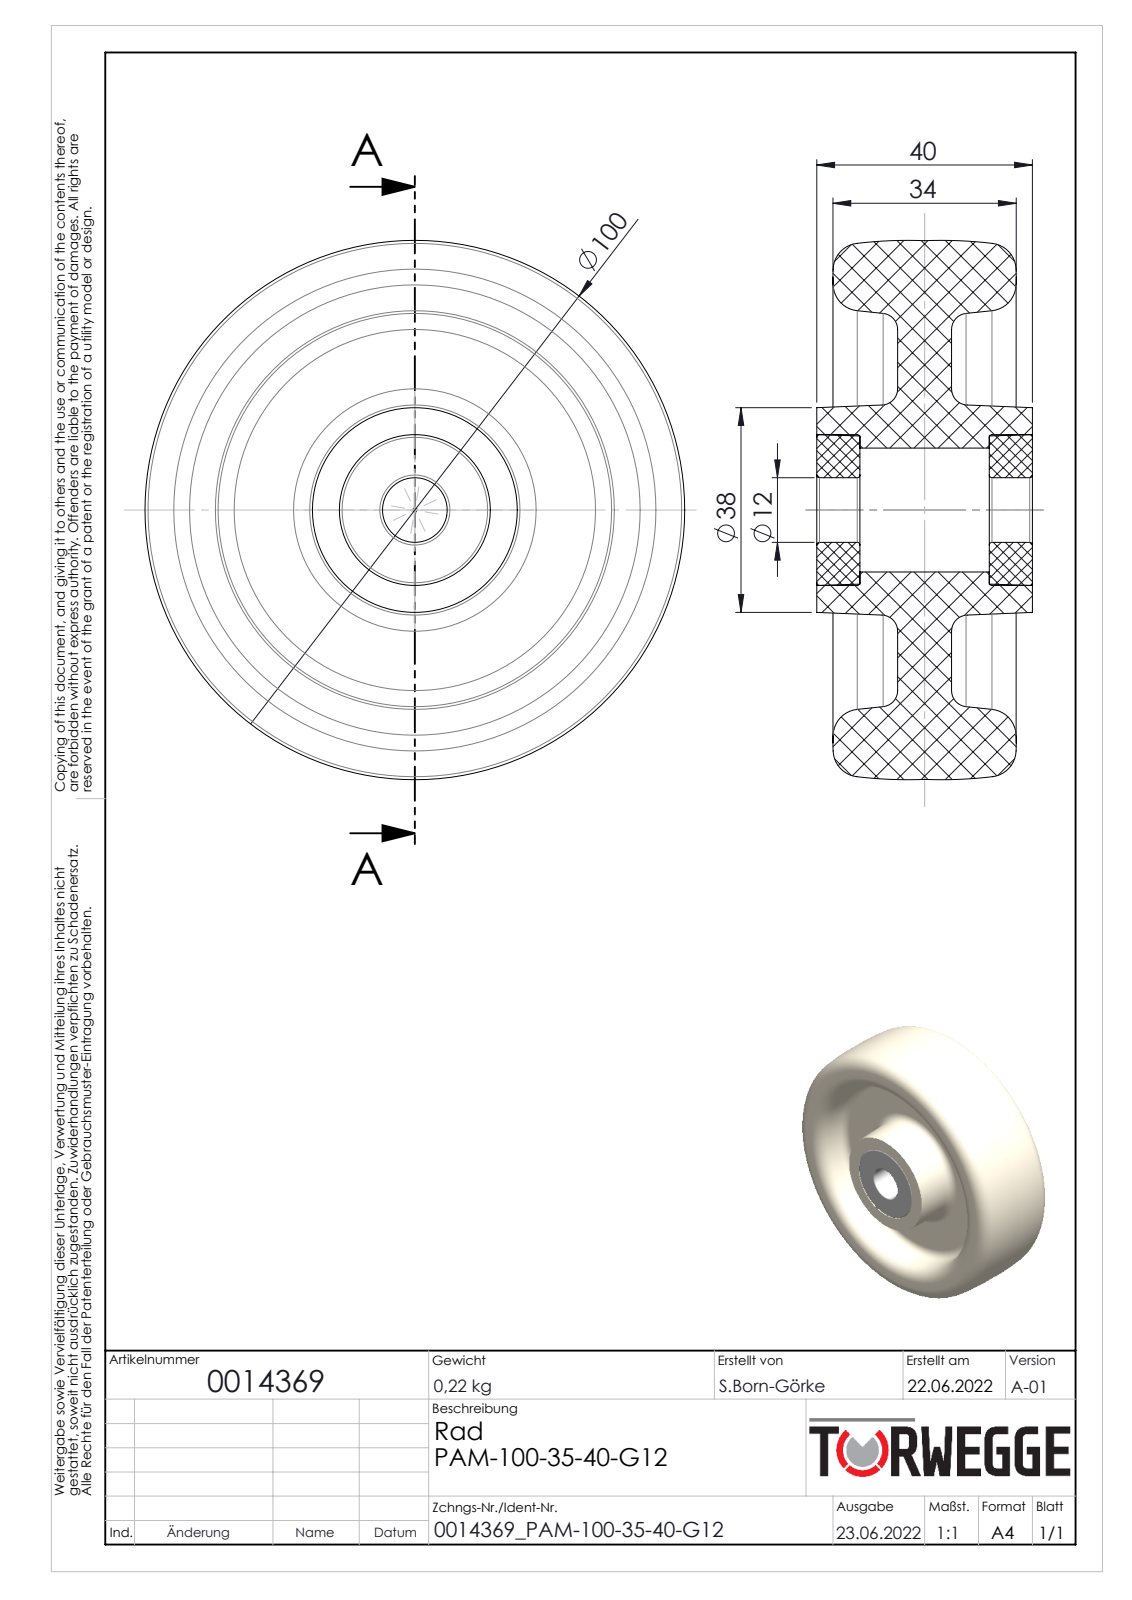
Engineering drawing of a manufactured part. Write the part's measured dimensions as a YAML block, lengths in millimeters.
part_name: "0014369"
step_written_by: "SolidWorks 2020 (AUTOMOTIVE_DESIGN)"
units: millimeters
bodies: {solids: 3, faces: 72, planar: 10, cylindrical: 10, other: 52}
overall_size: [100.12, 100.12, 40]
volume: 181935
surface_area: 37843
round_holes:
  - {diameter: 12, count: 1}
  - {diameter: 23, count: 1}
round_bosses_or_shafts:
  - {diameter: 28, count: 1}
face_to_face_distances: [10, 15, 25, 8, 32, 7, 17, 40, 24]
